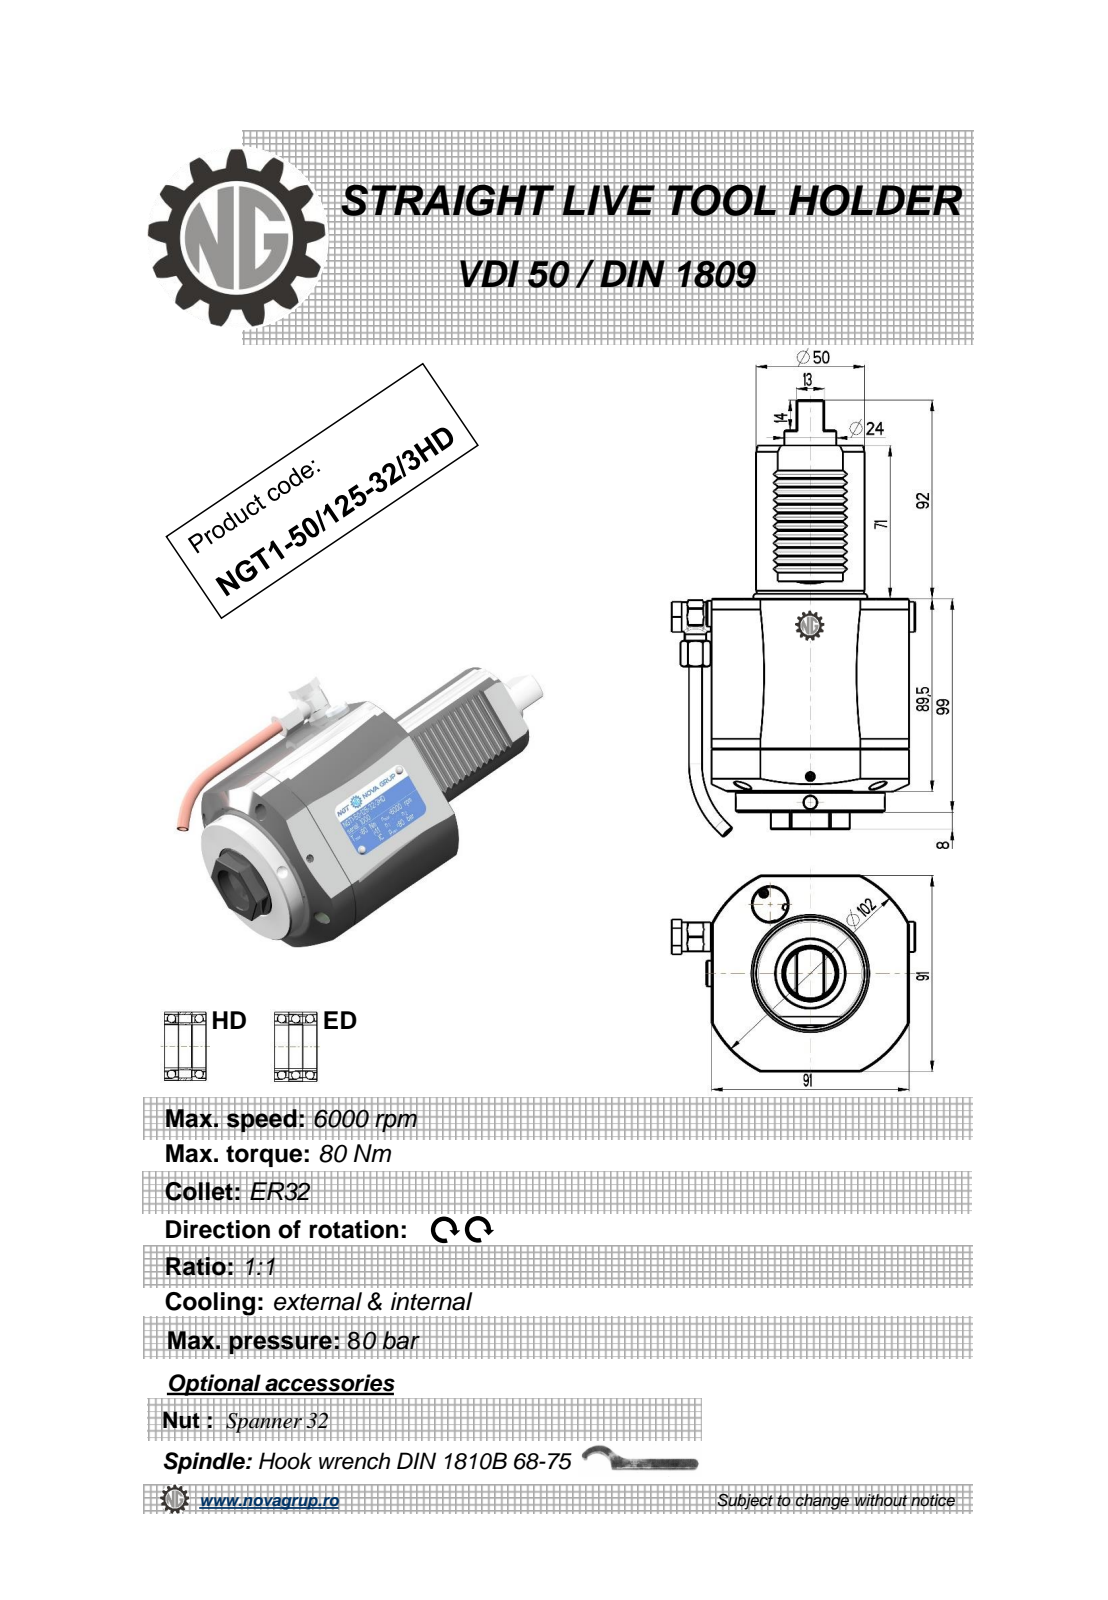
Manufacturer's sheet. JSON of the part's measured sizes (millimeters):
{"part_name": "NGT1_50_125_32_3HD", "step_written_by": "PRO/ENGINEER BY PARAMETRIC TECHNOLOGY CORPORATION, 2010280 (CONFIG_CONTROL_DESIGN)", "units": "millimeters", "bodies": {"solids": 1, "faces": 358, "planar": 150, "cylindrical": 96, "other": 112}, "overall_size": [202.44, 112.4, 91], "volume_mm3": 834429, "surface_area_mm2": 66270, "round_holes": [[4, 3], [6, 2], [3, 1], [6.2, 1], [9, 1], [10, 1], [11, 1], [23, 1], [34, 1]], "round_bosses_or_shafts": [[6, 2], [69, 1], [50, 1], [24, 1], [14, 1], [13.6, 1], [13, 1], [12, 1]], "partial_cylinders_radius": [[0.3, 12], [0.41, 6], [0.5, 4], [0.8, 2], [6.25, 1], [7.7, 1], [51, 1]], "face_to_face_distances": [91, 99, 9.5, 89.5, 170, 160.5, 71, 2.83, 14.14, 11.31], "hole_center_spacings": [0.4, 55.66, 56.04, 87.66]}
